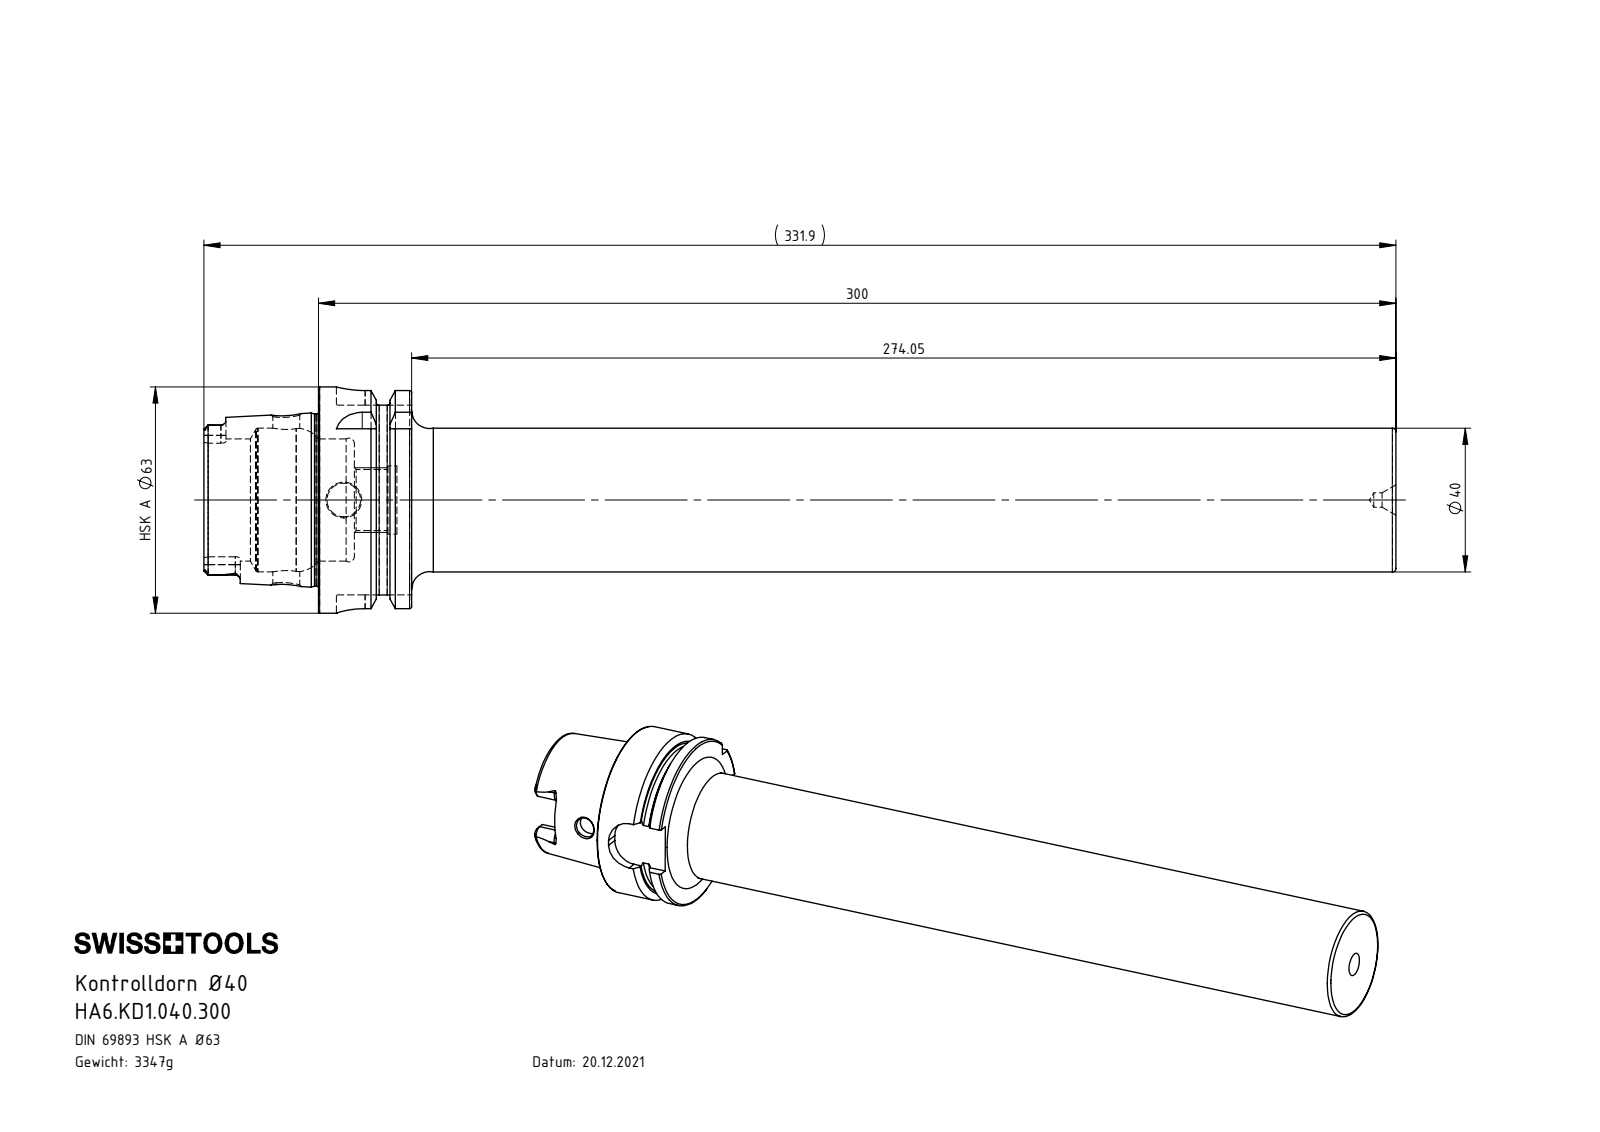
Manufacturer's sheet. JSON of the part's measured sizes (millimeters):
{"part_name": "6-K.1.040.300_A", "step_written_by": "SolidWorks 2017 (AUTOMOTIVE_DESIGN)", "units": "millimeters", "bodies": {"solids": 1, "faces": 158, "planar": 46, "cylindrical": 45, "other": 67}, "overall_size": [331.9, 63, 63], "volume_mm3": 426327, "surface_area_mm2": 56427, "round_holes": [[4, 1], [7.5, 1], [10, 1], [17, 1], [19, 1], [34, 1], [40, 1]], "round_bosses_or_shafts": [[63, 1], [54.95, 1], [47.93, 1]], "partial_cylinders_radius": [[1.4, 6], [2.88, 4], [8, 4]], "face_to_face_distances": [300, 25.95, 274.05, 16, 9.95, 290.05, 31.9, 41.85, 57.85, 331.9]}
